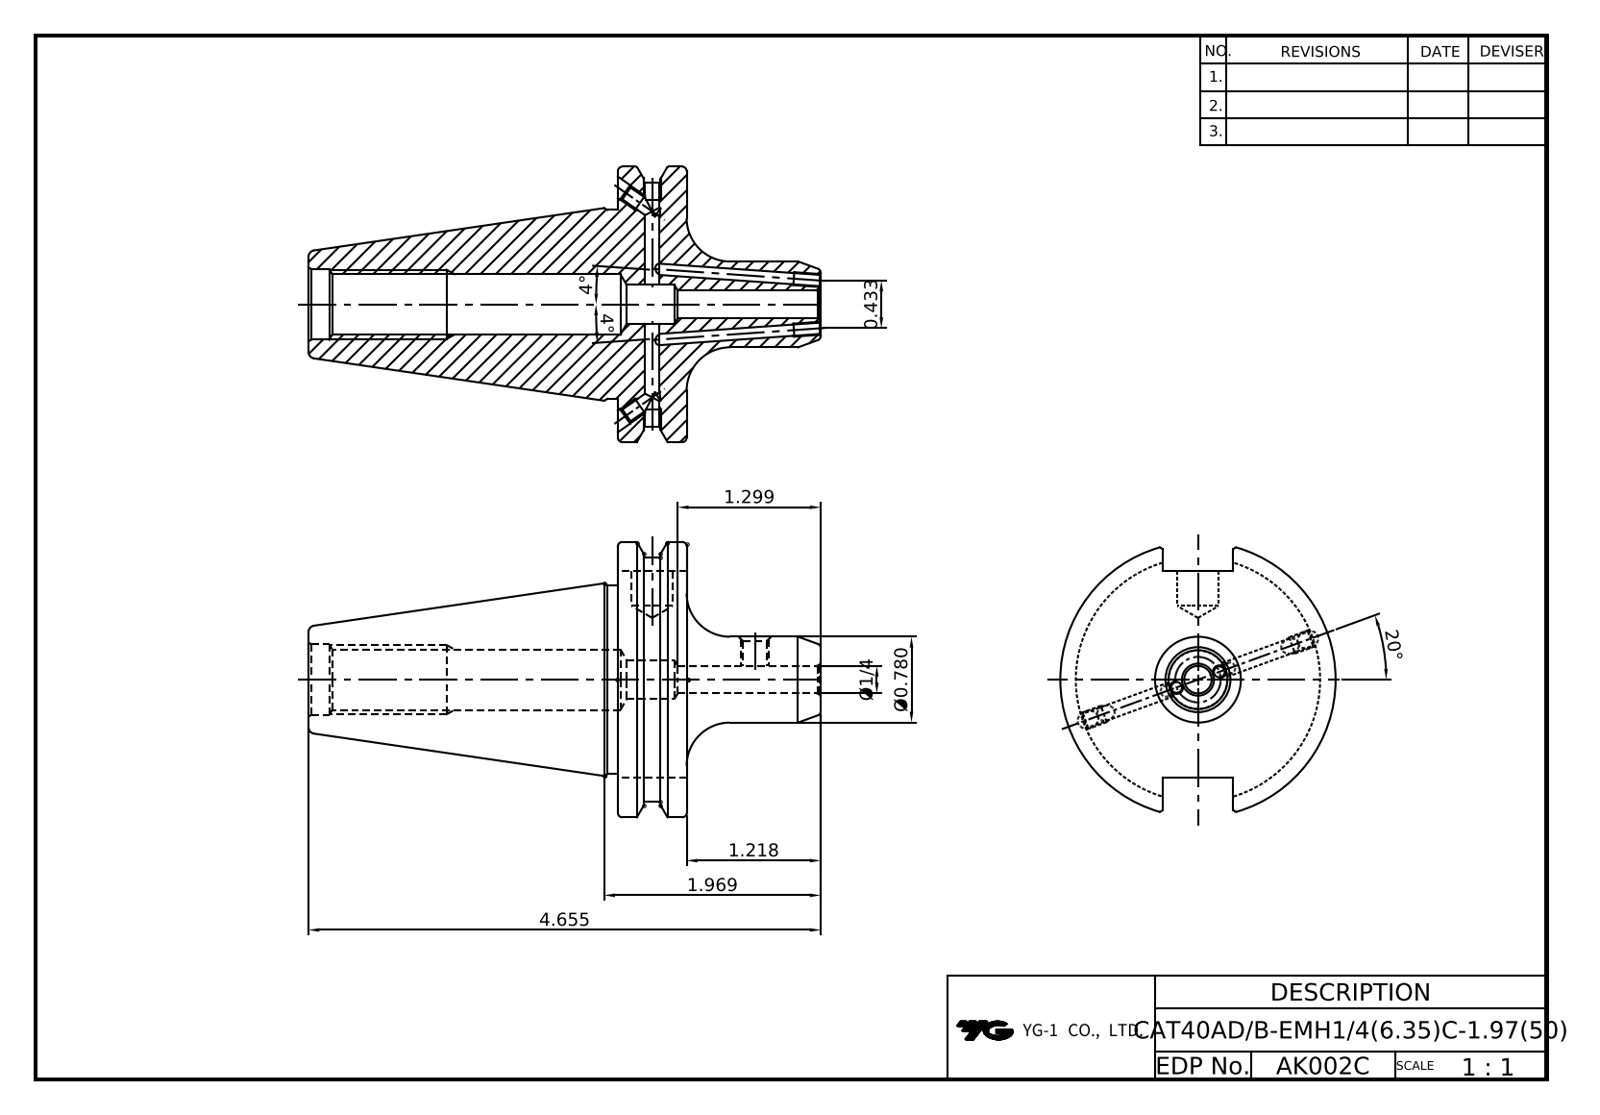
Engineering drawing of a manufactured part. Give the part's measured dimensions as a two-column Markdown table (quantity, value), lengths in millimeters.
| quantity | value |
| --- | --- |
| part name | CAT40ADB-EMH6.35C-50 |
| STEP written by | Autodesk Inventor 2022 (AUTOMOTIVE_DESIGN) |
| units | millimeters |
| bodies | 1 solid, 91 faces (36 planar, 31 cylindrical, 24 other) |
| overall size | 118.25 × 63.5 × 61.09 |
| volume | 110 626 mm³ |
| surface area | 23 711 mm² |
| round holes (diameter × count) | 3.24 × 4, 2.6 × 2, 4 × 2, 4.2 × 2, 5.36 × 1, 6.35 × 1, 9 × 1, 9.53 × 1, 13 × 1, 13.39 × 1, 16.3 × 1 |
| round bosses / shafts (diameter × count) | 63.5 × 1, 43.6 × 1, 19.81 × 1 |
| partial cylindrical surfaces (radius × count) | 28.15 × 1 |
| main face-to-face distances | 15.88, 47.6, 16.38, 71.42, 87.3, 118.25, 46.83, 30.95, 77.47, 6.05 |
| hole center spacings | 23.67 |
